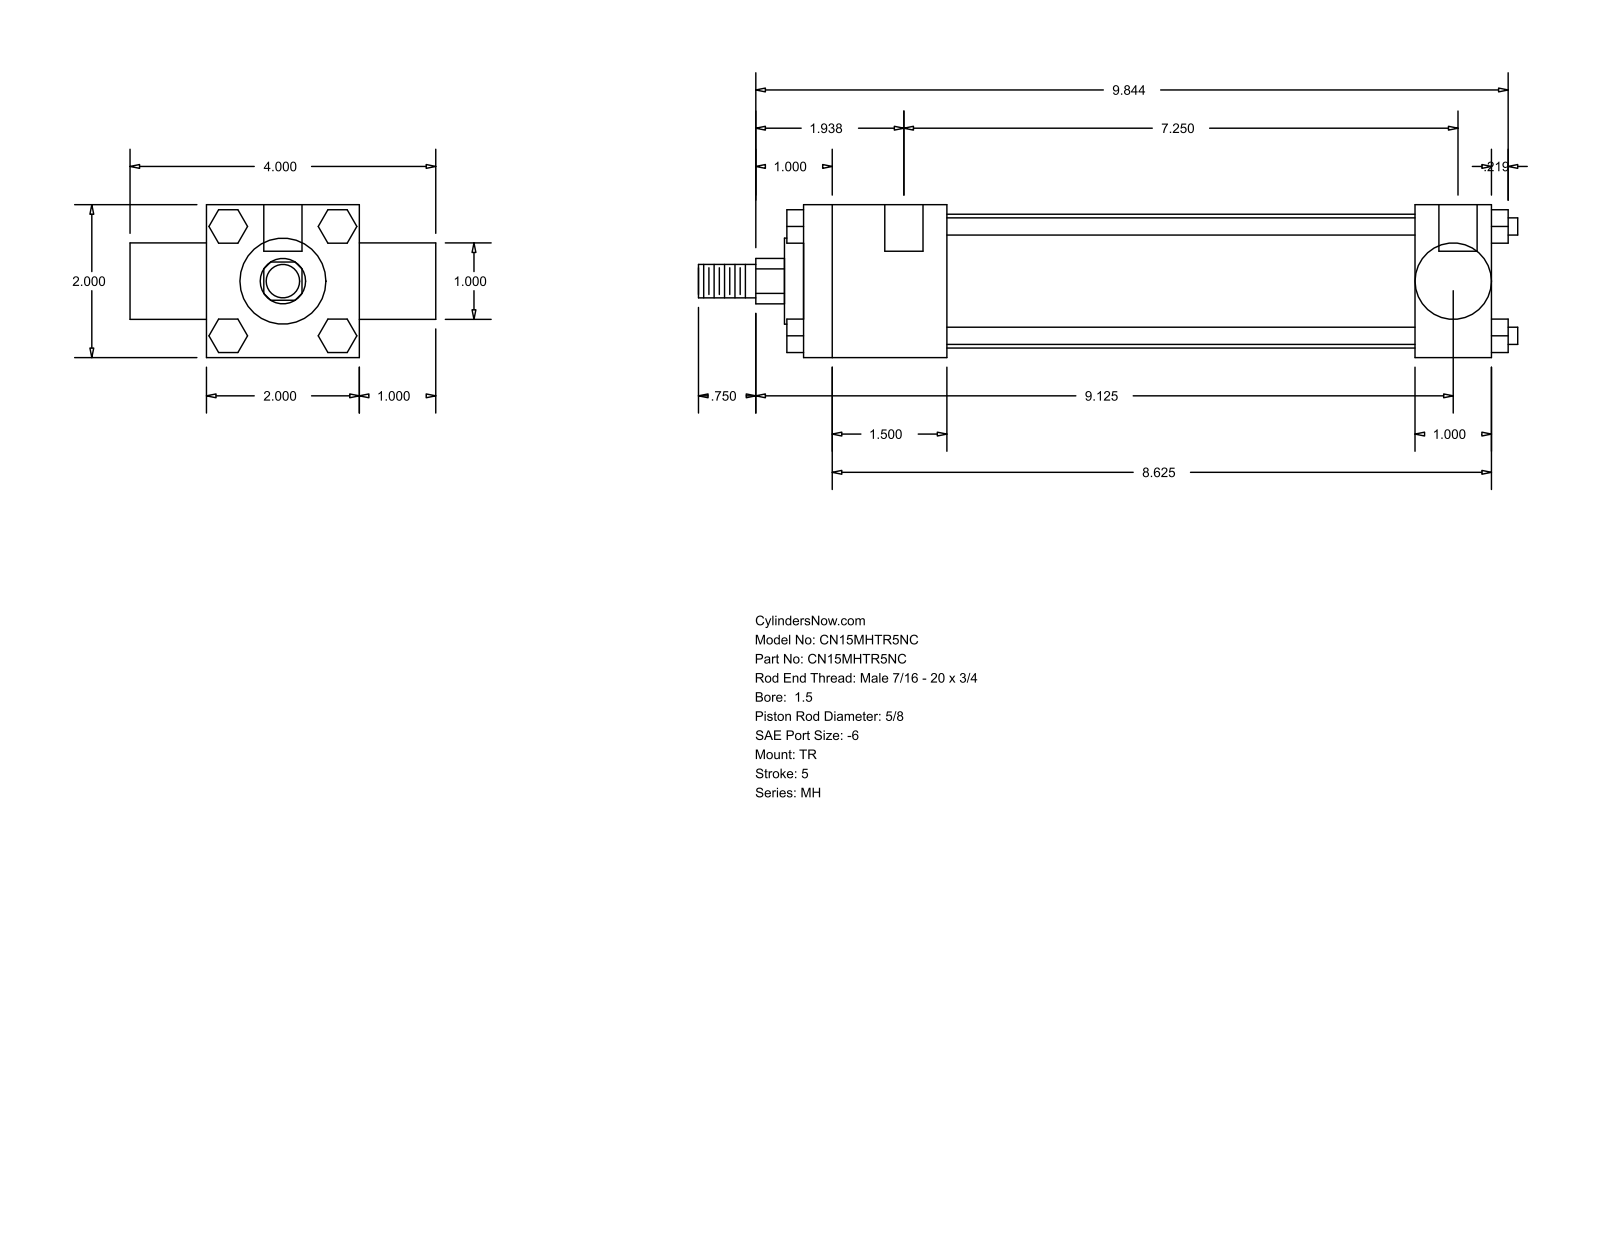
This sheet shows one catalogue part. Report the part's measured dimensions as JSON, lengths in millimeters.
{"part_name": "MH_TR__0150_0.625", "step_written_by": "GSSL Pune (CONFIG_CONTROL_DESIGN)", "units": "millimeters", "bodies": {"solids": 0, "faces": 120, "planar": 92, "cylindrical": 28, "other": 0}, "overall_size": [272.26, 101.6, 50.8], "round_holes": [[5.56, 3], [12.7, 2]], "round_bosses_or_shafts": [[5.71, 4], [44.45, 1], [28.57, 1], [25.35, 1], [15.88, 1], [11.11, 1]], "partial_cylinders_radius": [[7.54, 1]], "face_to_face_distances": [50.8, 25.4, 228.59, 76.2, 47.62, 180.97, 203.19, 155.57, 5.56, 234.15], "hole_center_spacings": [3.17, 184.15, 187.32]}
